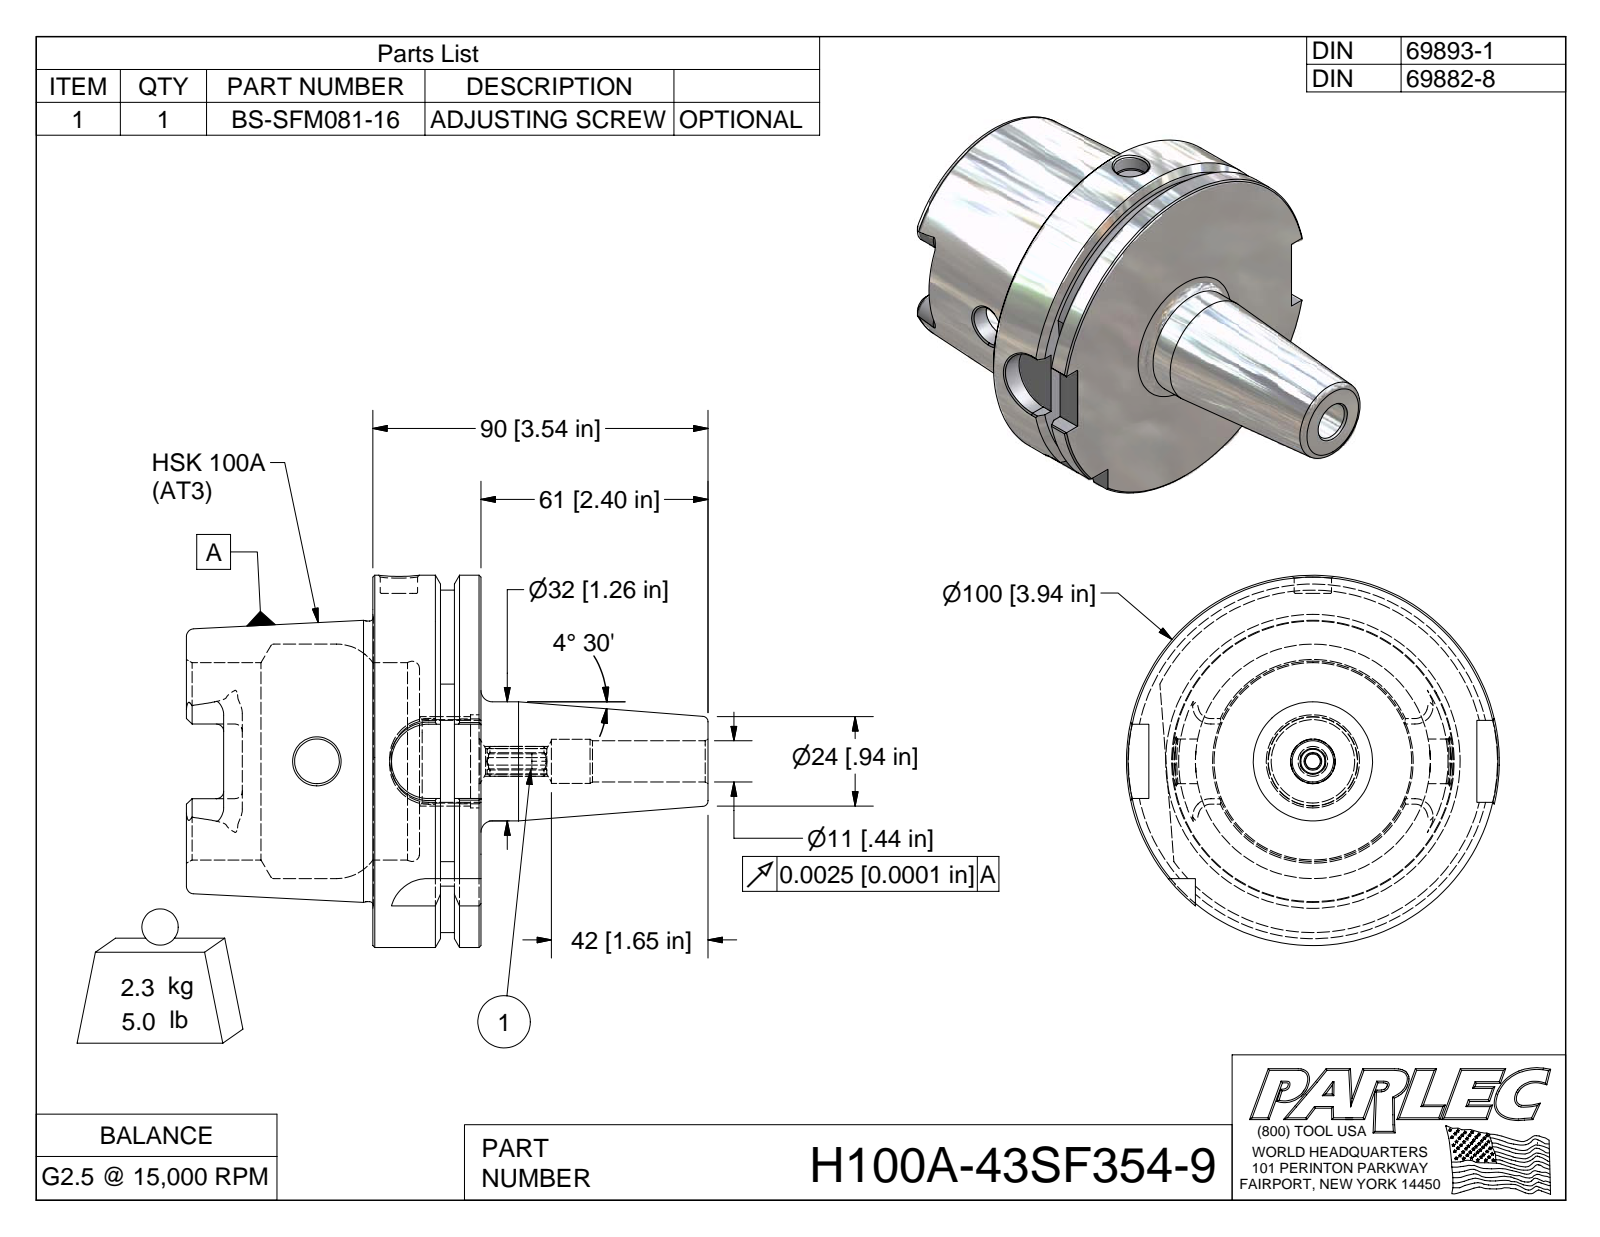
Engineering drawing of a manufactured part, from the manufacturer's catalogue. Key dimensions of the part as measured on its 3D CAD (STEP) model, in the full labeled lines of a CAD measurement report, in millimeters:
Part name (STEP PRODUCT): H100A-43SF354-9; H100A-43SF354-9-1; BS-SFM081-16
STEP written by: Autodesk Inventor 2009 (AUTOMOTIVE_DESIGN)
Units: millimetres
Bodies: 2 solids, 149 faces (49 planar, 30 cylindrical, 70 other)
Overall size (bounding box): 139.9 × 100 × 100
Volume: 289 100 mm³ · Surface area: 57 500 mm²
Round holes (diameter × count): ⌀10 ×1, ⌀11.1 ×1, ⌀11.9 ×1, ⌀12 ×1, ⌀22.4 ×1, ⌀25 ×1, ⌀53 ×1, ⌀63 ×1
Round bosses / shafts (diameter × count): ⌀100 ×1, ⌀75.4 ×1, ⌀32 ×1
Partial cylindrical surfaces — rounded edges, fillets, slot ends (radius × count): R10 ×4, R2 ×3, R4.9 ×2, R4 ×1, R46 ×1
Main face-to-face distances: 29, 12.5, 16.5, 50, 62.5, 79, 68.1, 18.1, 5.6, 10.9
